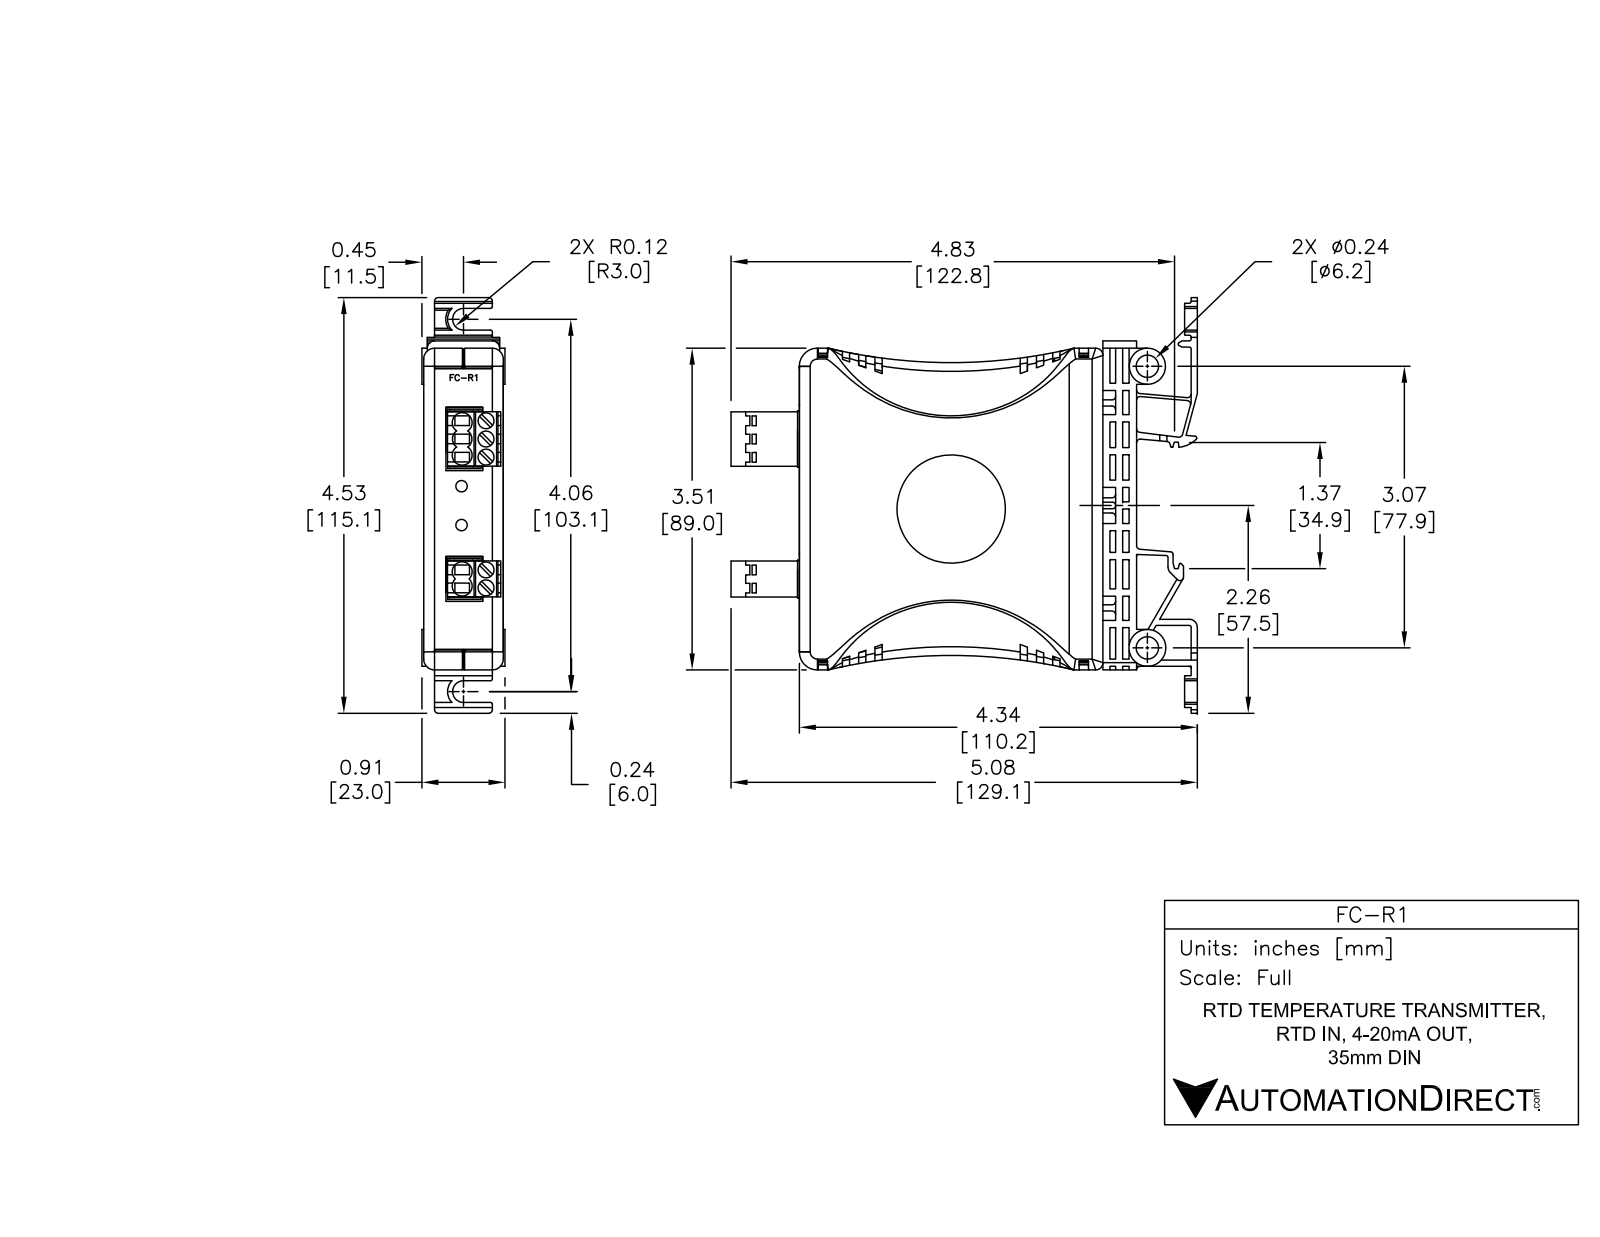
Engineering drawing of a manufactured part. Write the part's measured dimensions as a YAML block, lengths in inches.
part_name: "FC-ISO-C r1b Case Only 1 red1 fXT -surf1 COMPLETE 1 FC-R1 pre coord"
step_written_by: "SolidWorks 2017 (AUTOMOTIVE_DESIGN)"
units: inches
bodies: {solids: 13, faces: 2327, planar: 1730, cylindrical: 367, other: 230}
overall_size: [4.549, 4.34, 0.929]
volume: 3.634
surface_area: 120.5
round_holes:
  - {diameter: 0.01, count: 5}
  - {diameter: 0.016, count: 4}
  - {diameter: 0.045, count: 3}
  - {diameter: 0.124, count: 2}
  - {diameter: 0.244, count: 2}
  - {diameter: 0.045, count: 1}
  - {diameter: 1.181, count: 1}
round_bosses_or_shafts:
  - {diameter: 0.071, count: 5}
  - {diameter: 0.118, count: 4}
  - {diameter: 0.52, count: 1}
  - {diameter: 0.402, count: 1}
  - {diameter: 0.394, count: 1}
partial_cylinders:
  - {radius: 0.012, count: 28}
  - {radius: 0.02, count: 23}
  - {radius: 0.014, count: 16}
  - {radius: 0.039, count: 15}
  - {radius: 0.055, count: 10}
  - {radius: 0.118, count: 8}
  - {radius: 5.831, count: 6}
  - {radius: 0.138, count: 5}
face_to_face_distances: [0.063, 0.803, 0.06, 0.624, 0.683, 0.56, 0.62, 0.119, 0.739, 0.179]
hole_center_spacings: [1.426, 0.017, 0.197, 1.23, 1.623, 0.198, 0.197, 0.425]
